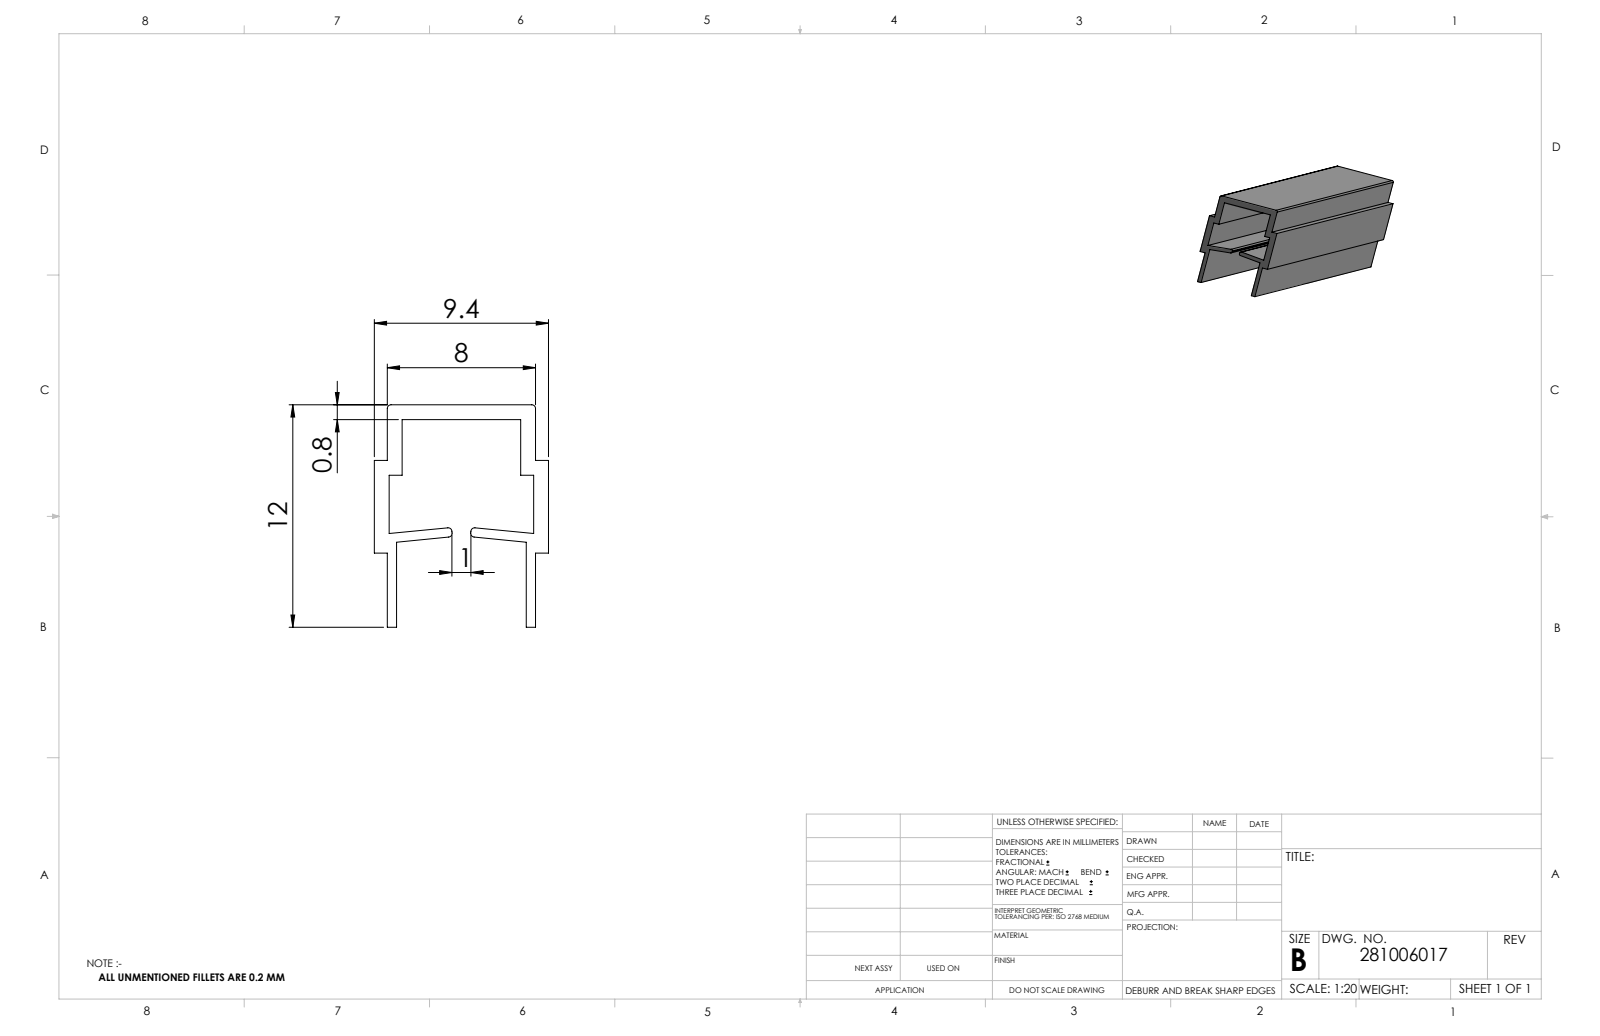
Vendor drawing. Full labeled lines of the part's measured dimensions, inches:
Part name (STEP PRODUCT): 281006017_c_1
STEP written by: SolidWorks 2014 (CONFIG_CONTROL_DESIGN)
Units: inches
Bodies: 1 solid, 37 faces (30 planar, 7 cylindrical, 0 other)
Overall size (bounding box): 78.74 × 0.472 × 0.37
Volume: 3.28 in³ · Surface area: 243 in²
Partial cylindrical surfaces — rounded edges, fillets, slot ends (radius × count): R0.008 ×6
Main face-to-face distances: 0.031, 0.028, 0.311, 0.323, 0.343, 0.047, 0.02, 0.295, 0.315, 0.283
